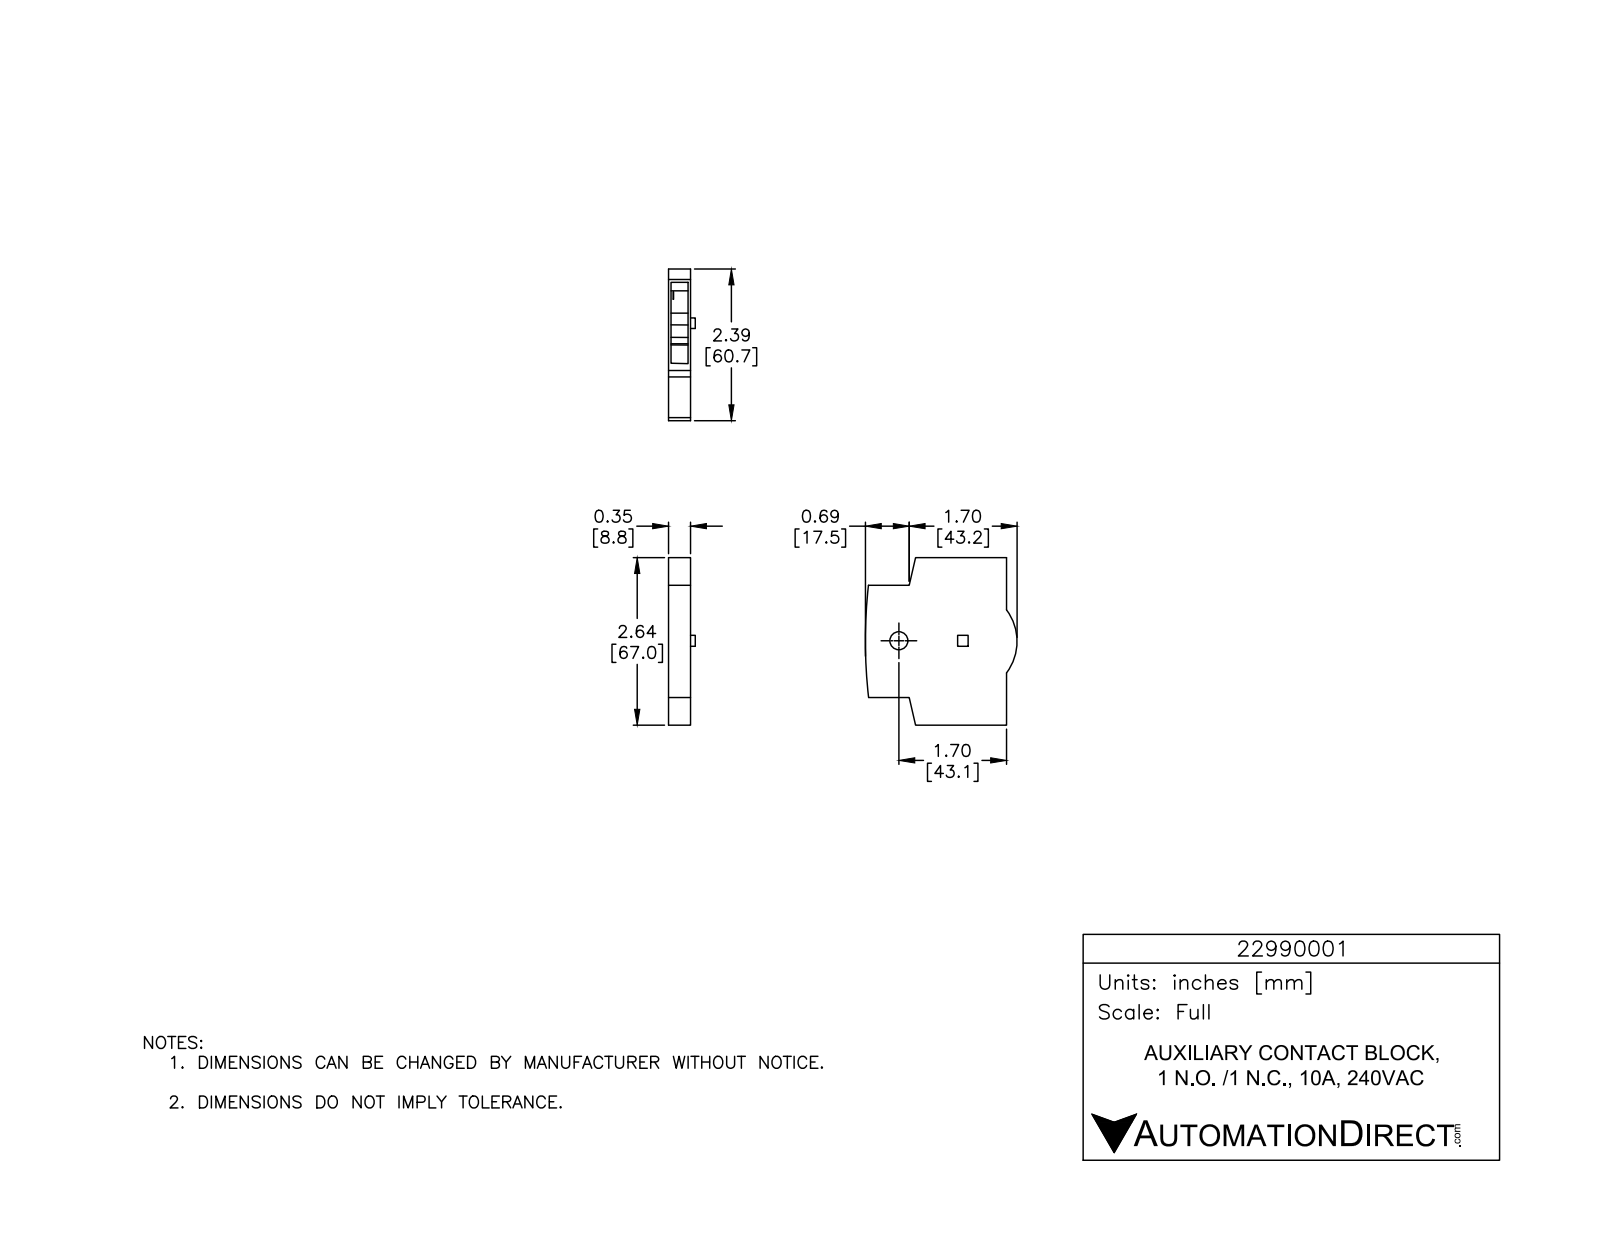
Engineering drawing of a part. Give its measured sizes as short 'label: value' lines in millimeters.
name: 22990001-UL
written by: SolidWorks 2021 (CONFIG_CONTROL_DESIGN)
unit: mm
bodies: 1 solid, 56 faces (52 planar, 1 cylindrical, 3 other)
size: 67 × 60.7 × 10.7
volume: 27 510 mm³; area: 10 330 mm²
rounds: 1× R21
face distances: 8.8, 1, 7.8, 6.8, 11, 56, 44.9, 67, 19.6, 9.4
